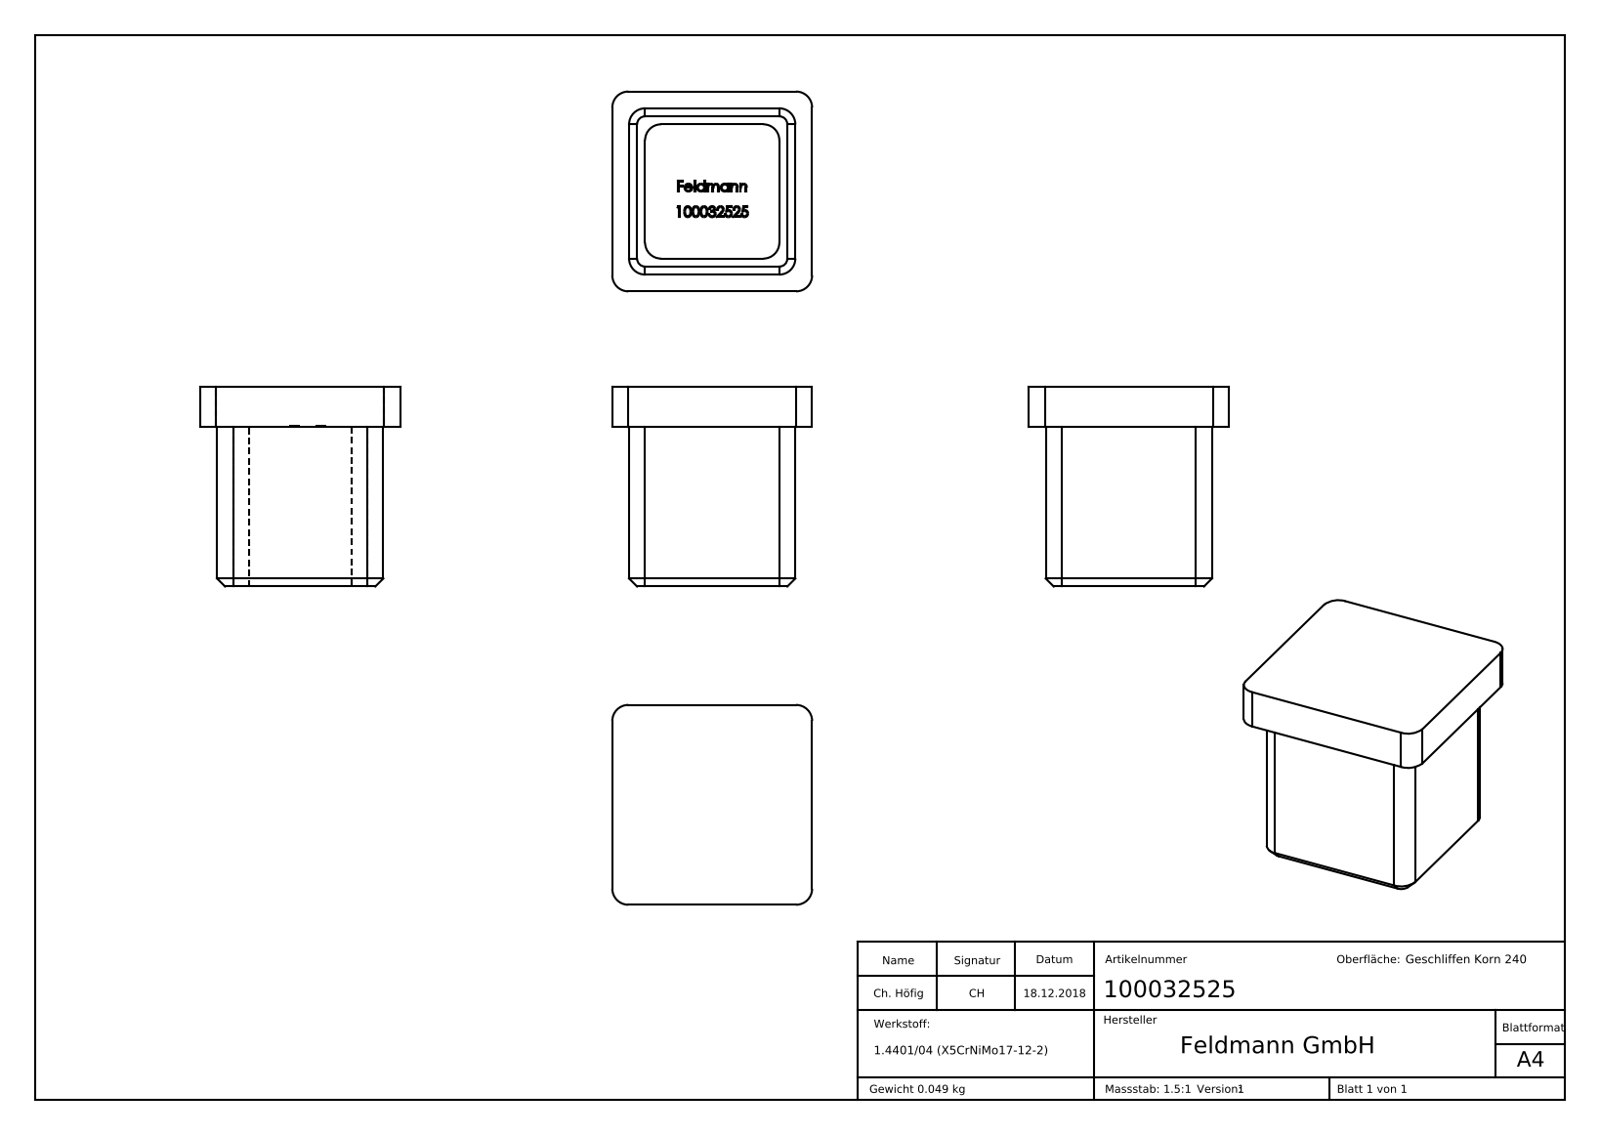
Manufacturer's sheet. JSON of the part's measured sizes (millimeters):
{"part_name": "100032525", "step_written_by": "SolidWorks 2015 (CONFIG_CONTROL_DESIGN)", "units": "millimeters", "bodies": {"solids": 1, "faces": 263, "planar": 130, "cylindrical": 12, "other": 121}, "overall_size": [25, 25, 25], "volume_mm3": 6076, "surface_area_mm2": 4559, "partial_cylinders_radius": [[2, 12]], "face_to_face_distances": [2, 18.8, 20.8, 16.8, 5, 2.1, 4.1, 20.9, 22.9, 25]}
